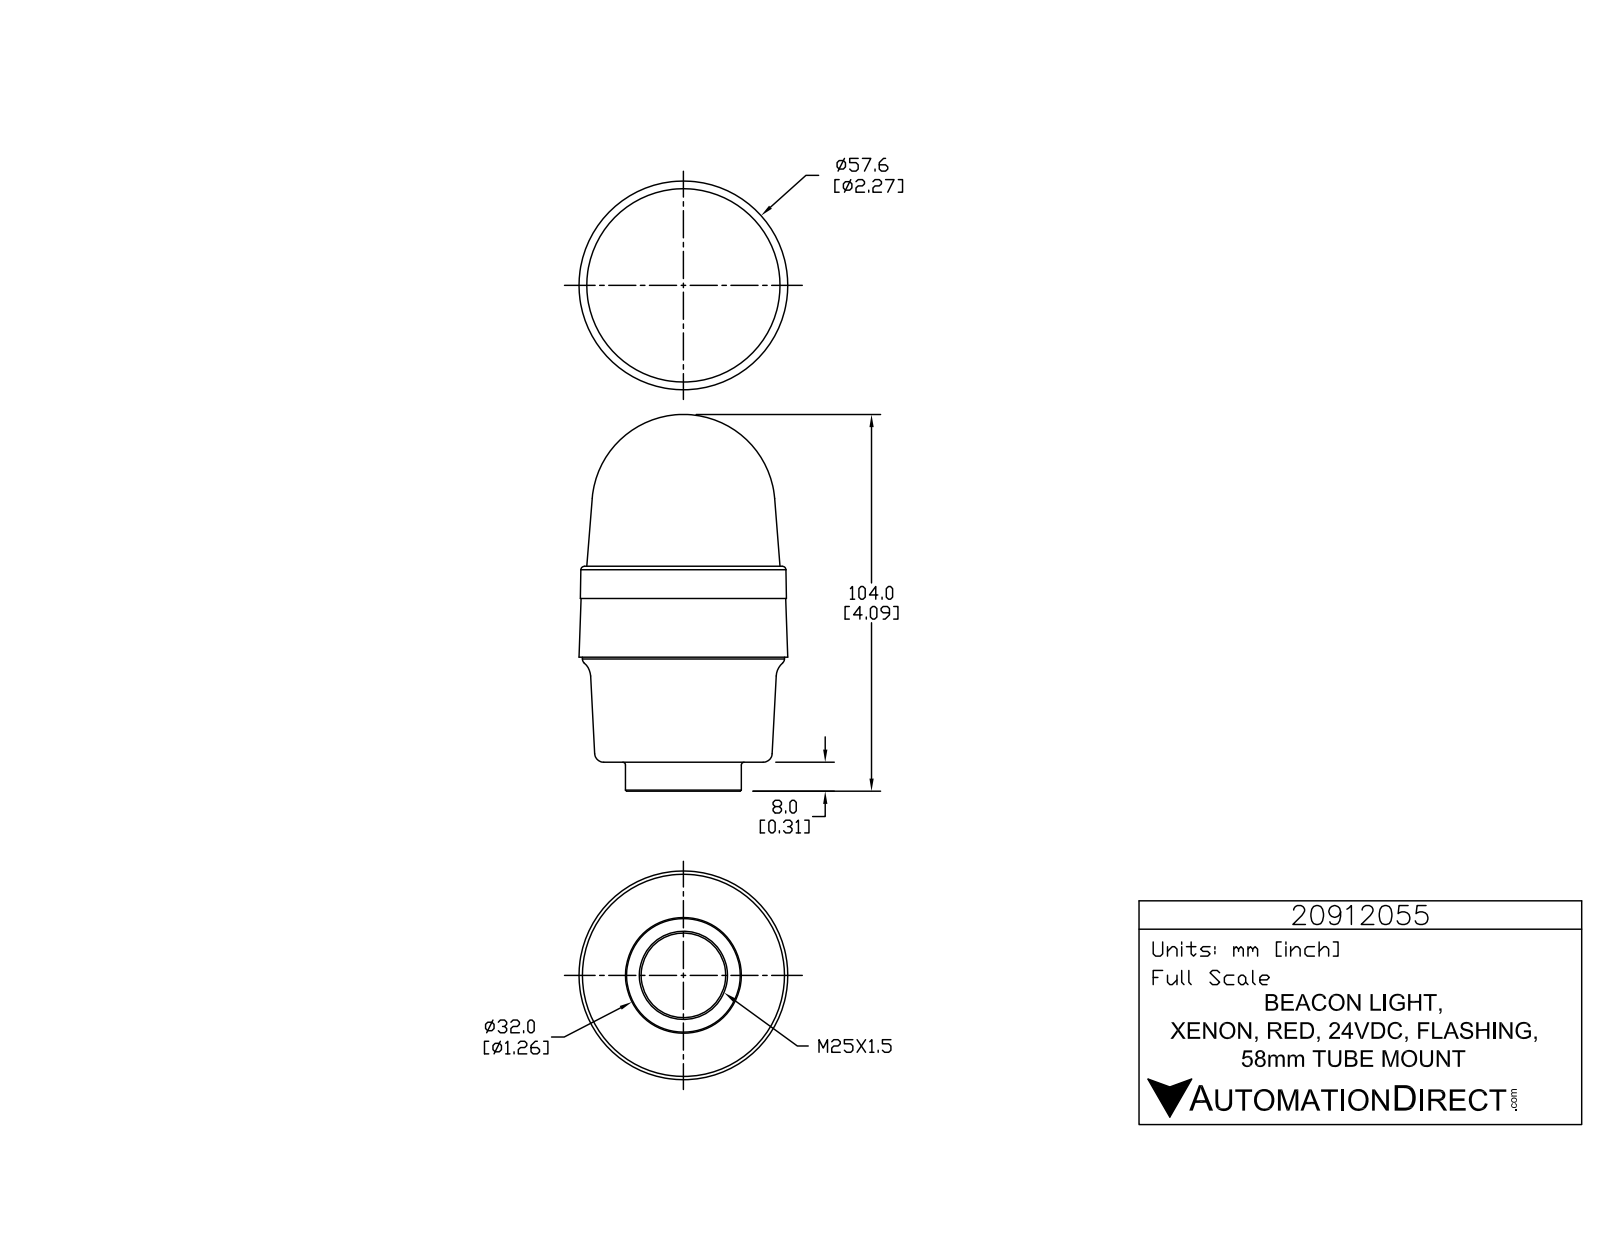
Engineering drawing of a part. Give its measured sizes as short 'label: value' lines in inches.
name: 20912055
written by: SolidWorks 2015 (AUTOMOTIVE_DESIGN)
unit: in
bodies: 1 solid, 791 faces (525 planar, 168 cylindrical, 98 other)
size: 4.051 × 2.269 × 2.269
volume: 11.72 in³; area: 29.93 in²
holes: 3× ⌀0.039, 1× ⌀0.92
bosses: 3× ⌀0.226, 3× ⌀0.056, 1× ⌀2.197, 1× ⌀1.26
rounds: 6× R0.008, 6× R0.008, 6× R0.008, 6× R0.131, 3× R0.004, 3× R0.005, 3× R0.008, 3× R0.008
face distances: 0.315, 1.142, 1.457, 0.988, 2.13, 2.445, 0.35, 0.638, 1.78, 2.094
